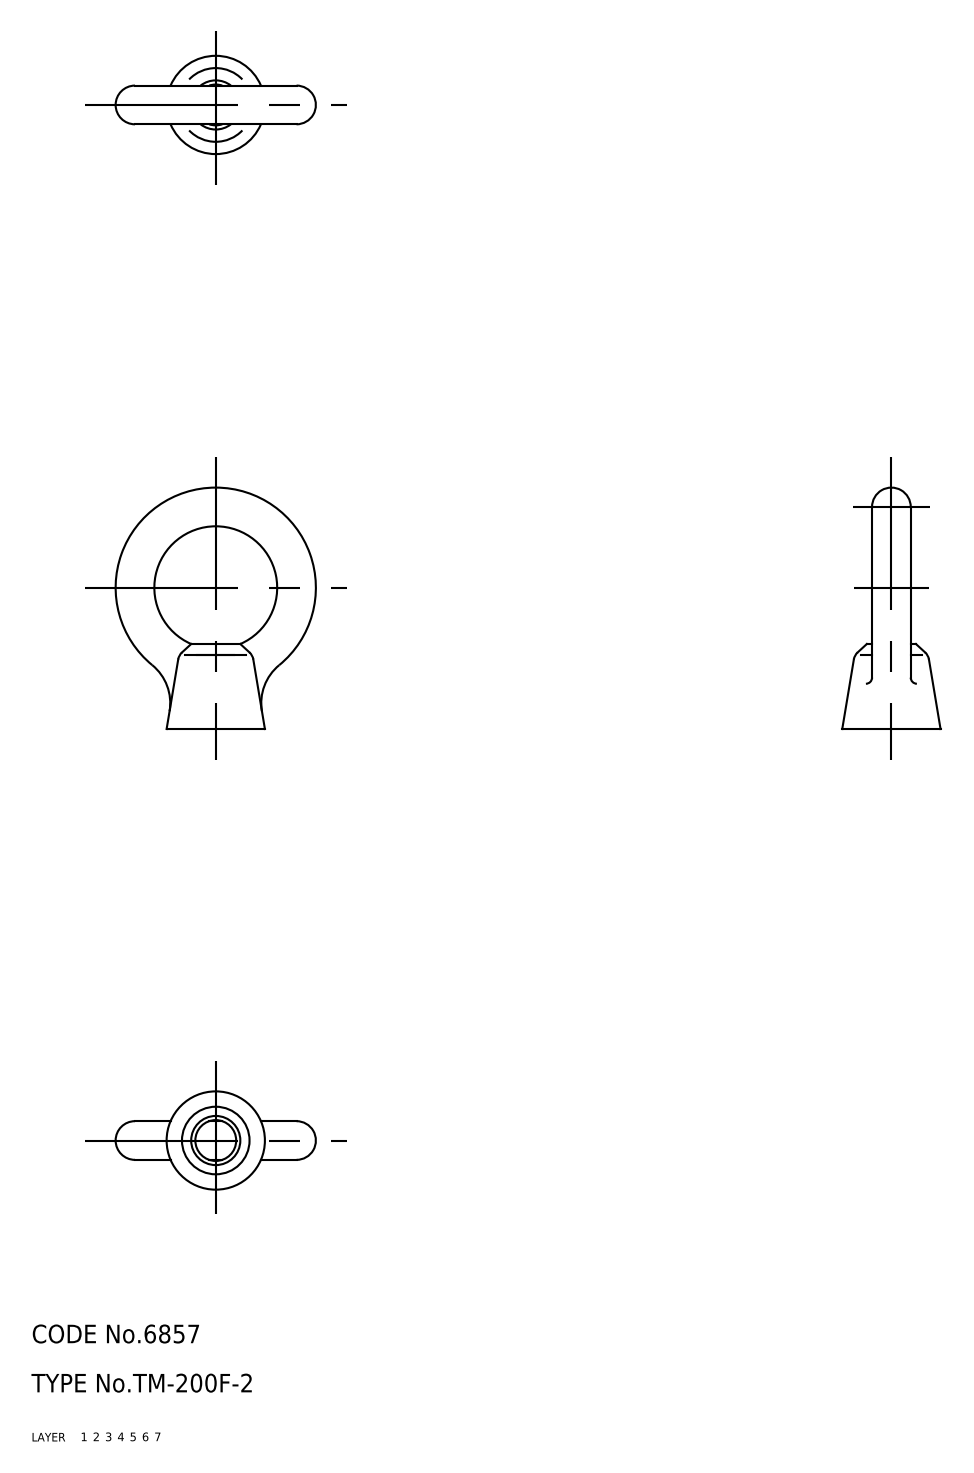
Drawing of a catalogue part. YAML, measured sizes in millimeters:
part_name: "TM_200F_2"
step_written_by: "SolidWorks 2003240 (AUTOMOTIVE_DESIGN)"
units: millimeters
bodies: {solids: 1, faces: 19, planar: 1, cylindrical: 2, other: 16}
overall_size: [39.3, 32.6, 16]
volume: 3574
surface_area: 2448
round_holes:
  - {diameter: 8, count: 1}
